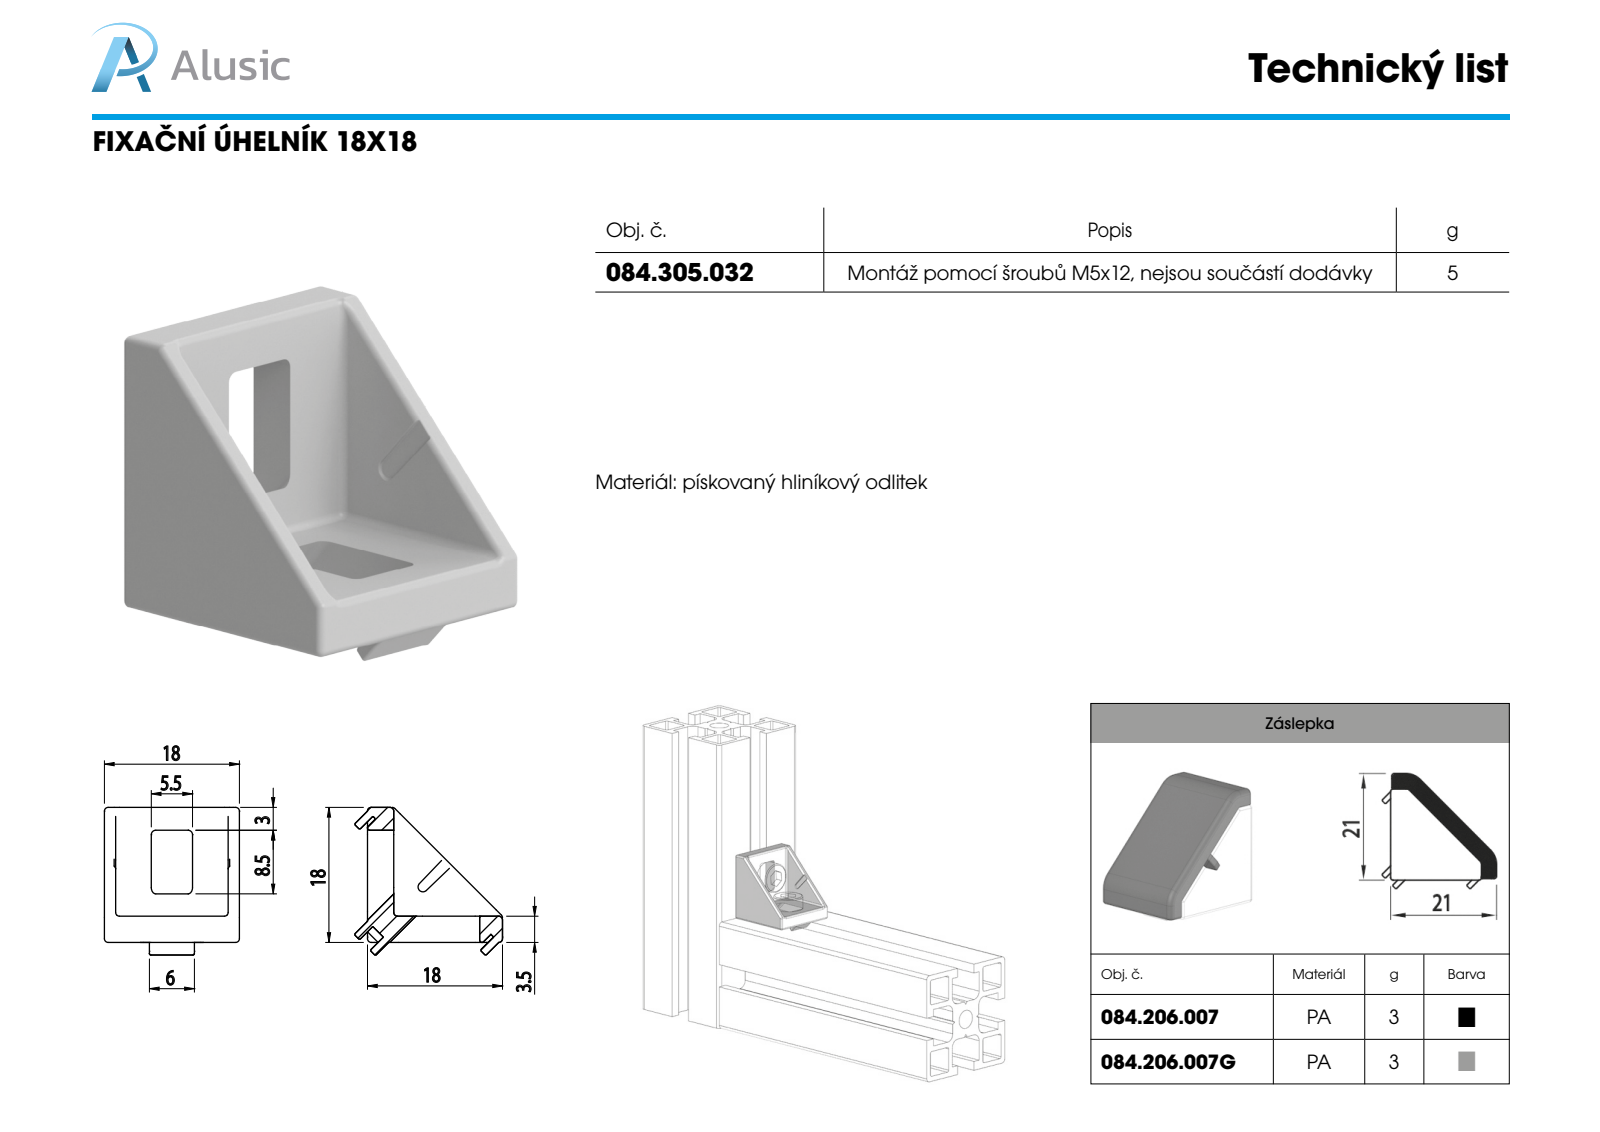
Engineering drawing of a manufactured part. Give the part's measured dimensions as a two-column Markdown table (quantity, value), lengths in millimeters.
| quantity | value |
| --- | --- |
| part name | 084.305.032 |
| STEP written by | SolidWorks 2016 (CONFIG_CONTROL_DESIGN) |
| units | millimeters |
| bodies | 1 solid, 425 faces (81 planar, 188 cylindrical, 156 other) |
| overall size | 19.68 × 19.68 × 18 |
| volume | 1 810 mm³ |
| surface area | 2 068 mm² |
| partial cylindrical surfaces (radius × count) | 0.2 × 55, 0.5 × 36, 0.1 × 22, 0.6 × 20, 0.3 × 16 |
| main face-to-face distances | 18, 1.5, 3.5, 16.5, 10.25, 6.25, 11.75, 4.75, 14.5, 15 |
